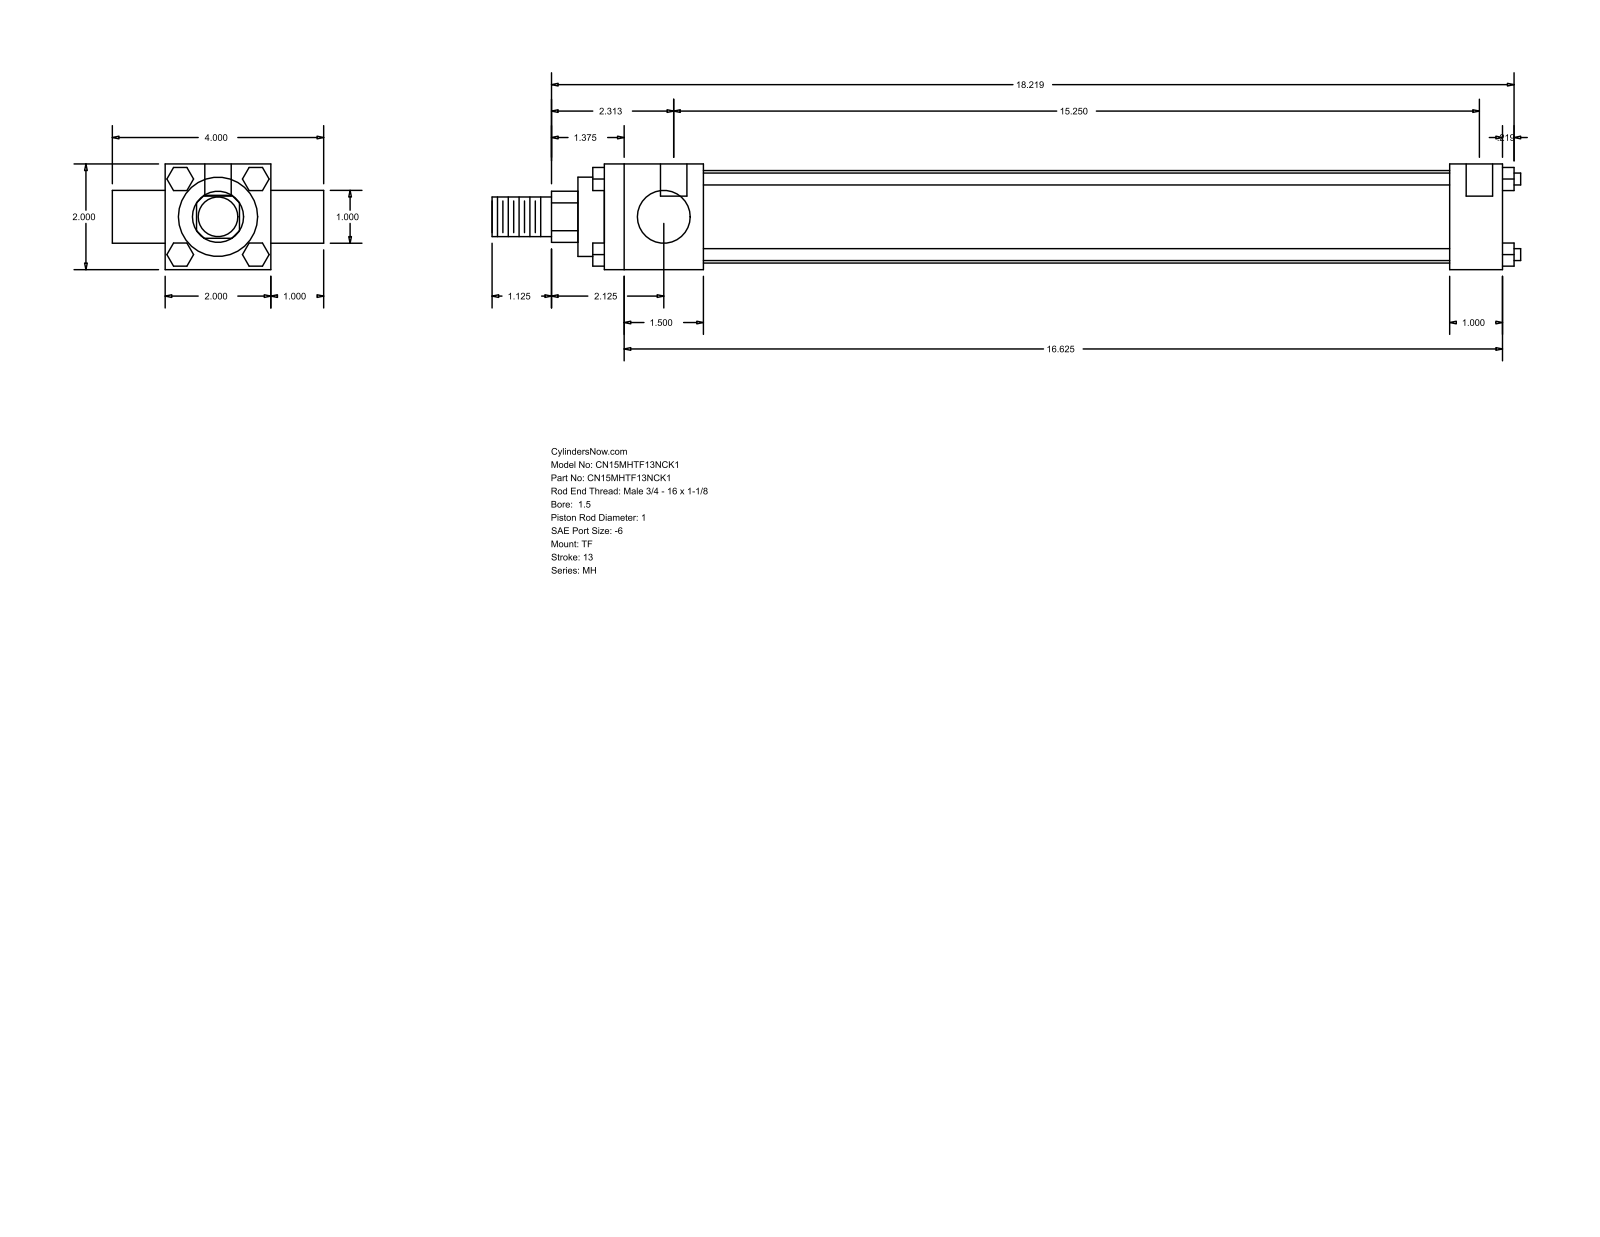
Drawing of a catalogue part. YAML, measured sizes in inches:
part_name: "MH_TF__0150_1"
step_written_by: "GSSL Pune (CONFIG_CONTROL_DESIGN)"
units: inches
bodies: {solids: 0, faces: 120, planar: 92, cylindrical: 28, other: 0}
overall_size: [19.469, 4, 2]
round_holes:
  - {diameter: 0.219, count: 3}
  - {diameter: 0.5, count: 2}
round_bosses_or_shafts:
  - {diameter: 0.225, count: 4}
  - {diameter: 1, count: 2}
  - {diameter: 1.75, count: 1}
  - {diameter: 1.5, count: 1}
  - {diameter: 0.75, count: 1}
partial_cylinders:
  - {radius: 0.484, count: 1}
face_to_face_distances: [2, 1, 17, 3, 1.875, 15.125, 16, 14.125, 4, 0.5]
hole_center_spacings: [0.125, 15.25, 15.375]
